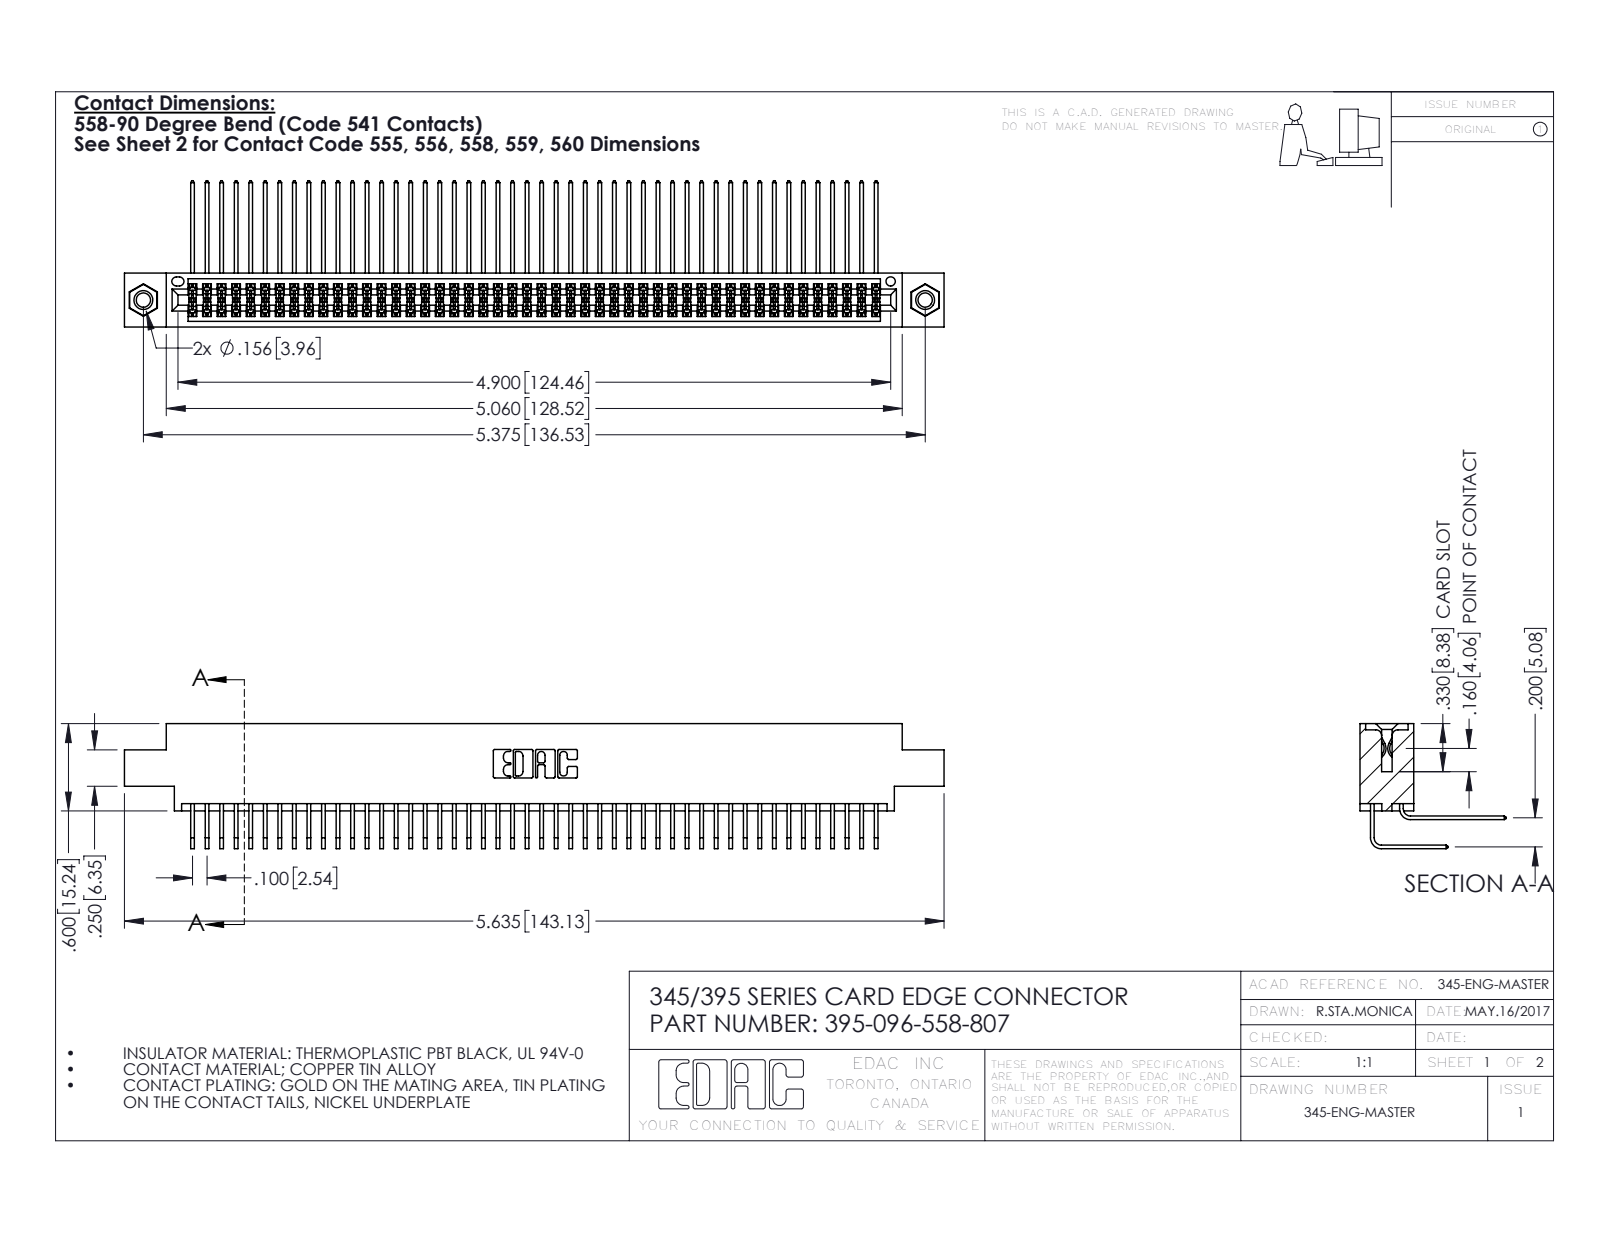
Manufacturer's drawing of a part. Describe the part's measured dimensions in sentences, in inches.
The part is named "345-250-001_345-250-005-103; 395-096-558-807; 345-292-001_558 Tail - 2; 345 Part_0.170 Offset - 0.156 Dia-TI (+1 more)". Its 3-D file was written by "SolidWorks 2016 (CONFIG_CONTROL_DESIGN)". It is 99 solids with 5182 faces: 3476 planar, 1690 cylindrical and 16 other. Overall it measures 5.635 by 1.005 by 0.859 inches. Its volume is 0.878 cubic inches and its surface area 37.44 square inches. Round holes: 2 of diameter 0.098, 2 of diameter 0.125, 2 of diameter 0.156, 1 of diameter 0.064. Round bosses or shafts: 2 of diameter 0.155. Partial cylindrical surfaces (rounded edges, fillets, slot ends): 145 of radius 0.006, 22 of radius 0.01, 6 of radius 0.007, 6 of radius 0.031, 3 of radius 0.026, 2 of radius 0.014, 2 of radius 0.019, 2 of radius 0.022. The main face-to-face distances are 0.072, 0.298, 0.2, 0.37, 0.098, 0.272, 0.025, 0.225, 0.175, 0.025. The hole center spacings are 0.27, 5.139, 5.375.
